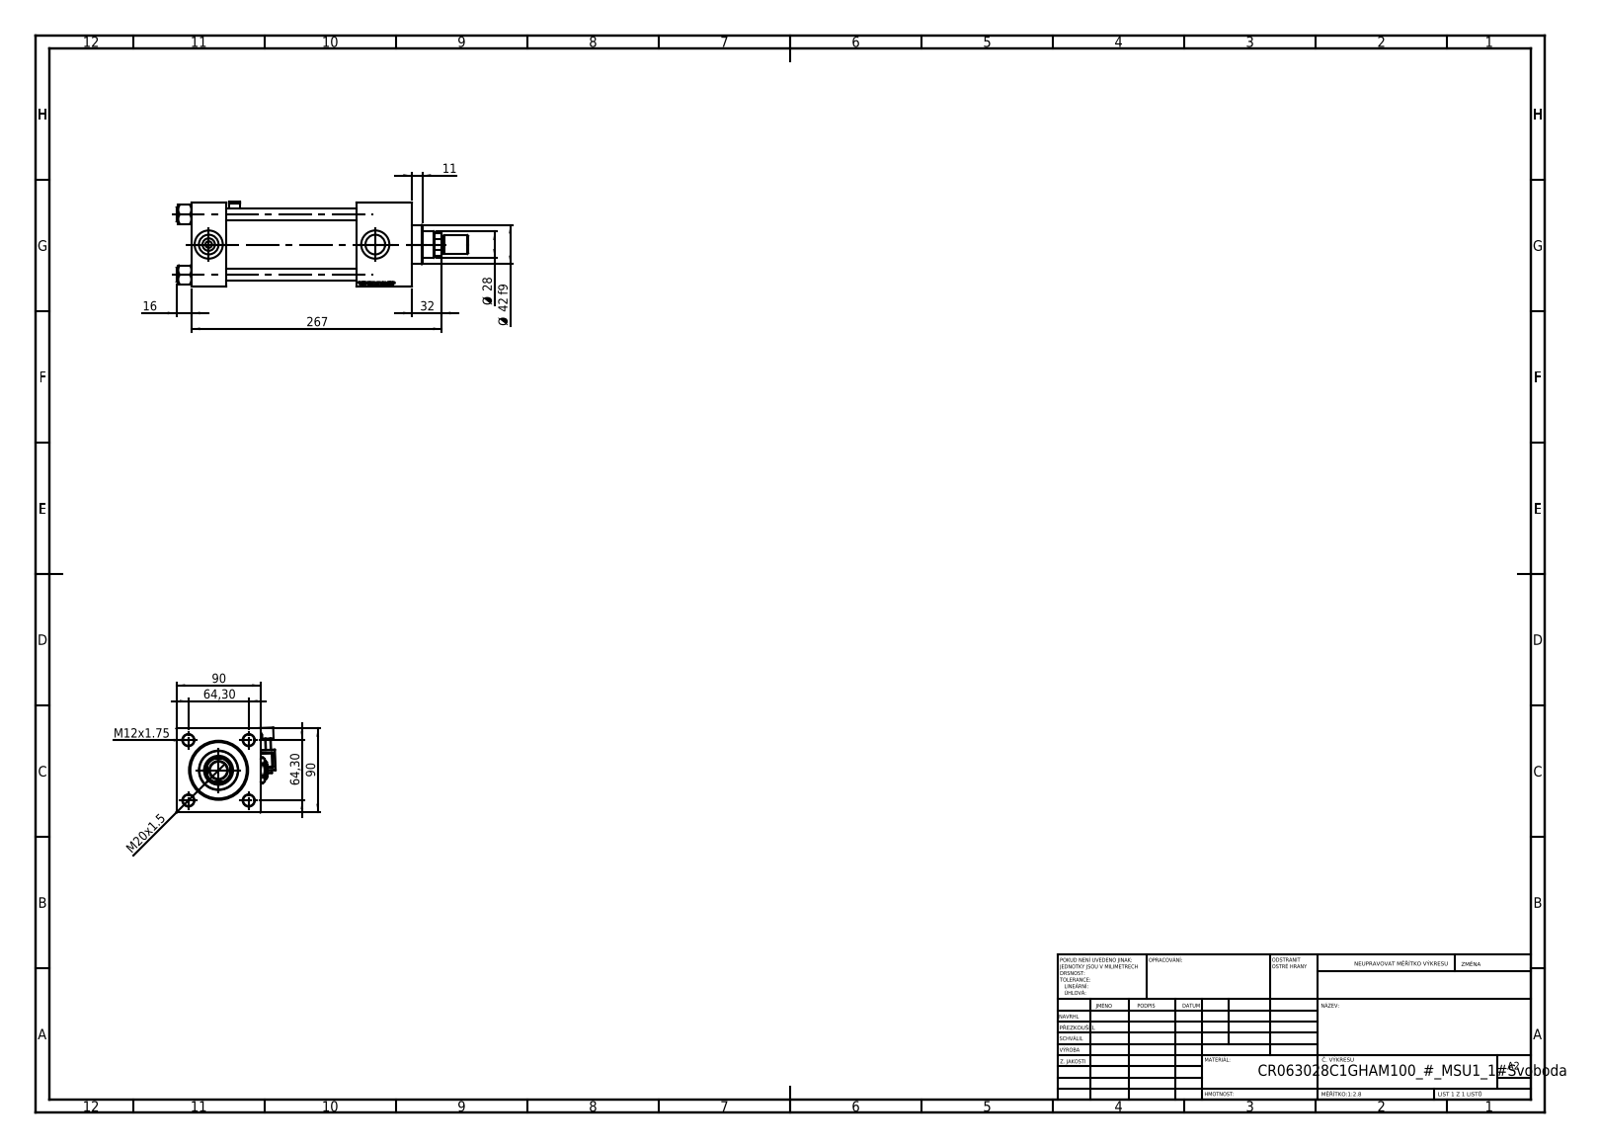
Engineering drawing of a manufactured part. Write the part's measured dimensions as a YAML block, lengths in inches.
part_name: "V215CR_C_Body; NUT_M5_C; V215CR_C_TYCINKA; V215CR_VCP_C (+4 more)"
step_written_by: "SolidWorks 2019 (CONFIG_CONTROL_DESIGN)"
units: inches
bodies: {solids: 14, faces: 1287, planar: 583, cylindrical: 124, other: 580}
overall_size: [12.244, 4.165, 3.564]
volume: 67.55
surface_area: 375.3
round_holes:
  - {diameter: 0.472, count: 4}
  - {diameter: 0.276, count: 2}
  - {diameter: 0.825, count: 2}
  - {diameter: 1.181, count: 2}
  - {diameter: 0.728, count: 1}
  - {diameter: 1.102, count: 1}
  - {diameter: 1.22, count: 1}
  - {diameter: 1.969, count: 1}
  - {diameter: 2.362, count: 1}
  - {diameter: 2.48, count: 1}
round_bosses_or_shafts:
  - {diameter: 0.591, count: 4}
  - {diameter: 2.717, count: 1}
  - {diameter: 1.654, count: 1}
  - {diameter: 0.787, count: 1}
  - {diameter: 0.709, count: 1}
  - {diameter: 0.236, count: 1}
partial_cylinders:
  - {radius: 0.02, count: 24}
  - {radius: 0.039, count: 1}
  - {radius: 0.098, count: 1}
  - {radius: 0.157, count: 1}
  - {radius: 0.531, count: 1}
face_to_face_distances: [3.543, 1.457, 9.252, 7.795, 6.929, 5.472, 2.323, 8.122, 6.665, 1.193]
hole_center_spacings: [1.79, 2.531, 3.58, 6.988]
